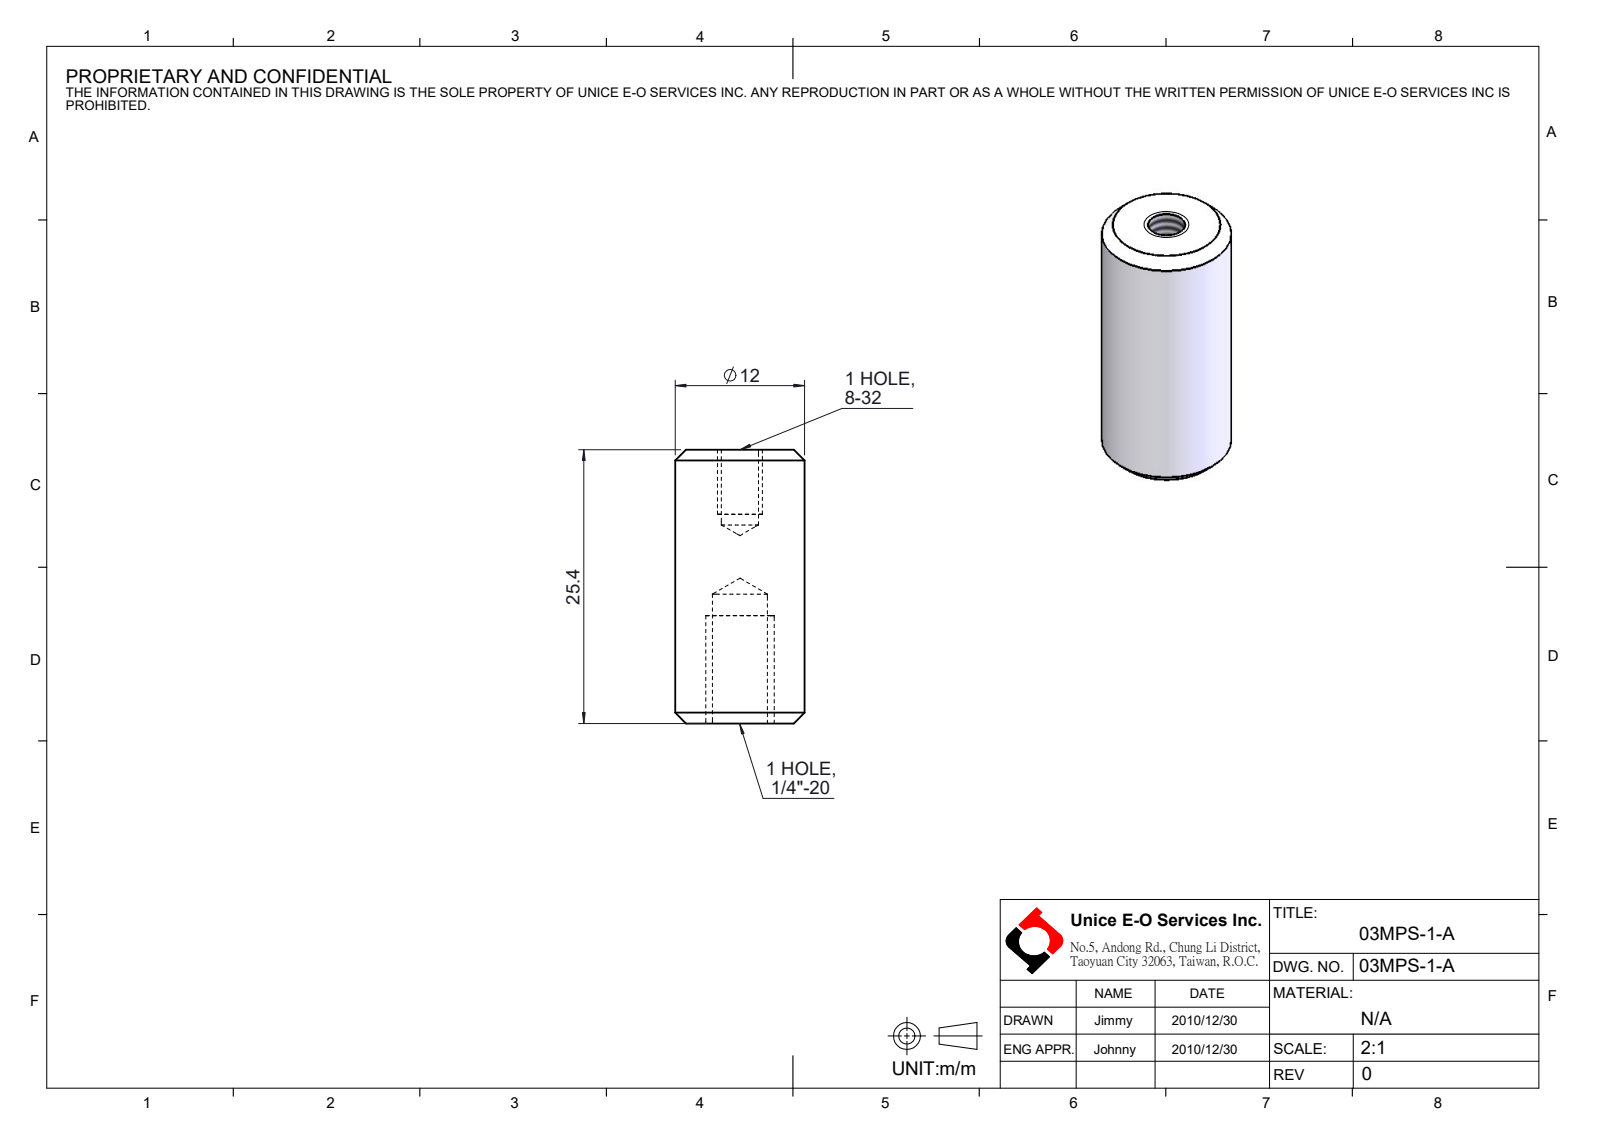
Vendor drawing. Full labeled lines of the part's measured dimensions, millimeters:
Part name (STEP PRODUCT): 03MPS-1-A
STEP written by: SolidWorks 2016 (CONFIG_CONTROL_DESIGN)
Units: millimetres
Bodies: 1 solid, 16 faces (2 planar, 6 cylindrical, 8 other)
Overall size (bounding box): 25.4 × 12 × 12
Volume: 2 513 mm³ · Surface area: 1 410 mm²
Round holes (diameter × count): ⌀3.45 ×1, ⌀5.11 ×1
Round bosses / shafts (diameter × count): ⌀12 ×1
Main face-to-face distances: 25.4
